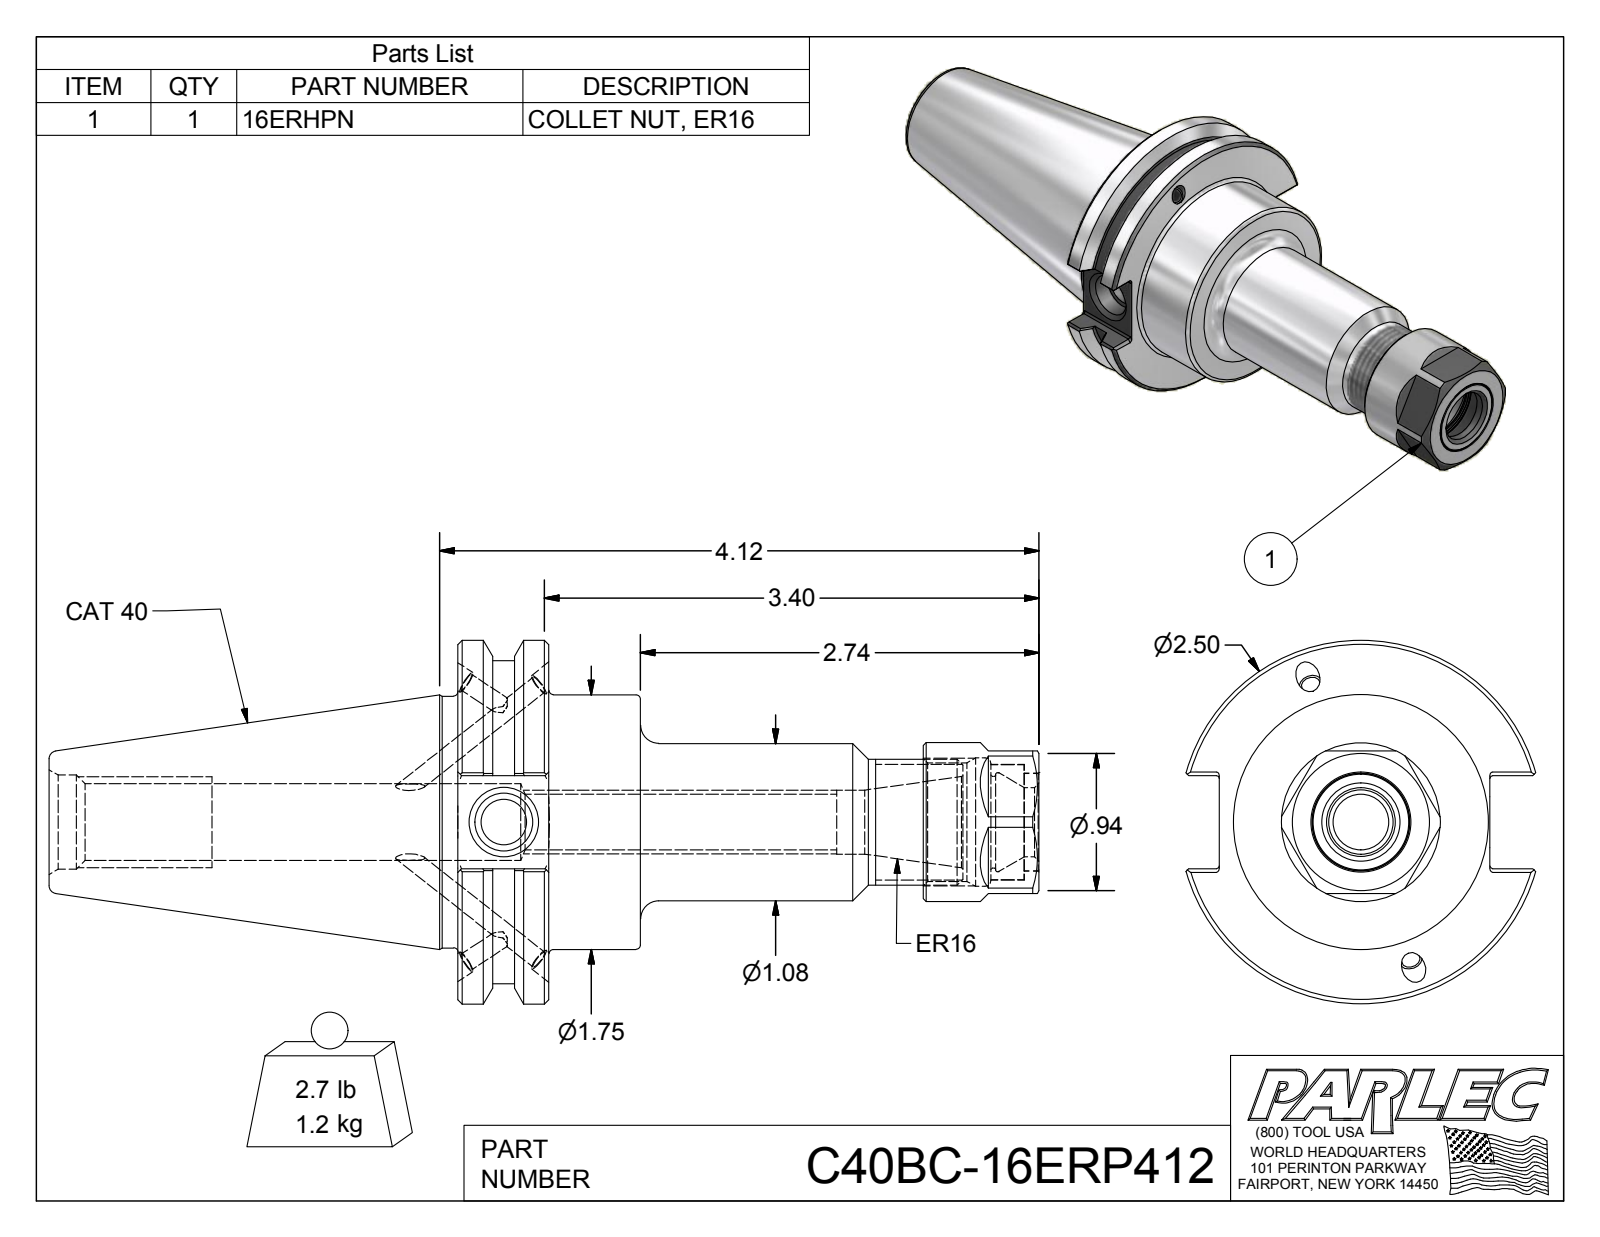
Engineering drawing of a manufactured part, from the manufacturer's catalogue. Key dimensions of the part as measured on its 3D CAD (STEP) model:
Part name (STEP PRODUCT): C40BCB-16ER4-1; 16ERHPN; 029-965; C40BC-16ERP412
STEP written by: Autodesk Inventor 2016 (AUTOMOTIVE_DESIGN)
Units: millimetres
Bodies: 7 solids, 216 faces (97 planar, 58 cylindrical, 61 other)
Overall size (bounding box): 172.9 × 63.5 × 61.11
Volume: 153 889 mm³ · Surface area: 35 104 mm²
Round holes (diameter × count): ⌀3.3 ×4, ⌀4.1 ×4, ⌀8 ×1, ⌀9.73 ×1, ⌀10.13 ×1, ⌀11.18 ×1, ⌀12.04 ×1, ⌀13.39 ×1, ⌀16 ×1, ⌀16.46 ×1, ⌀17.11 ×1, ⌀17.27 ×1
Round bosses / shafts (diameter × count): ⌀4.2 ×4, ⌀4 ×4, ⌀63.5 ×1, ⌀56.36 ×1, ⌀44.45 ×1, ⌀43.94 ×1, ⌀27.74 ×1, ⌀27.43 ×1
Partial cylindrical surfaces — rounded edges, fillets, slot ends (radius × count): R0.51 ×12
Main face-to-face distances: 15.87, 31.88, 16.01, 24.9, 101.47, 85.6, 69.59, 4.32, 20.58, 81.25
